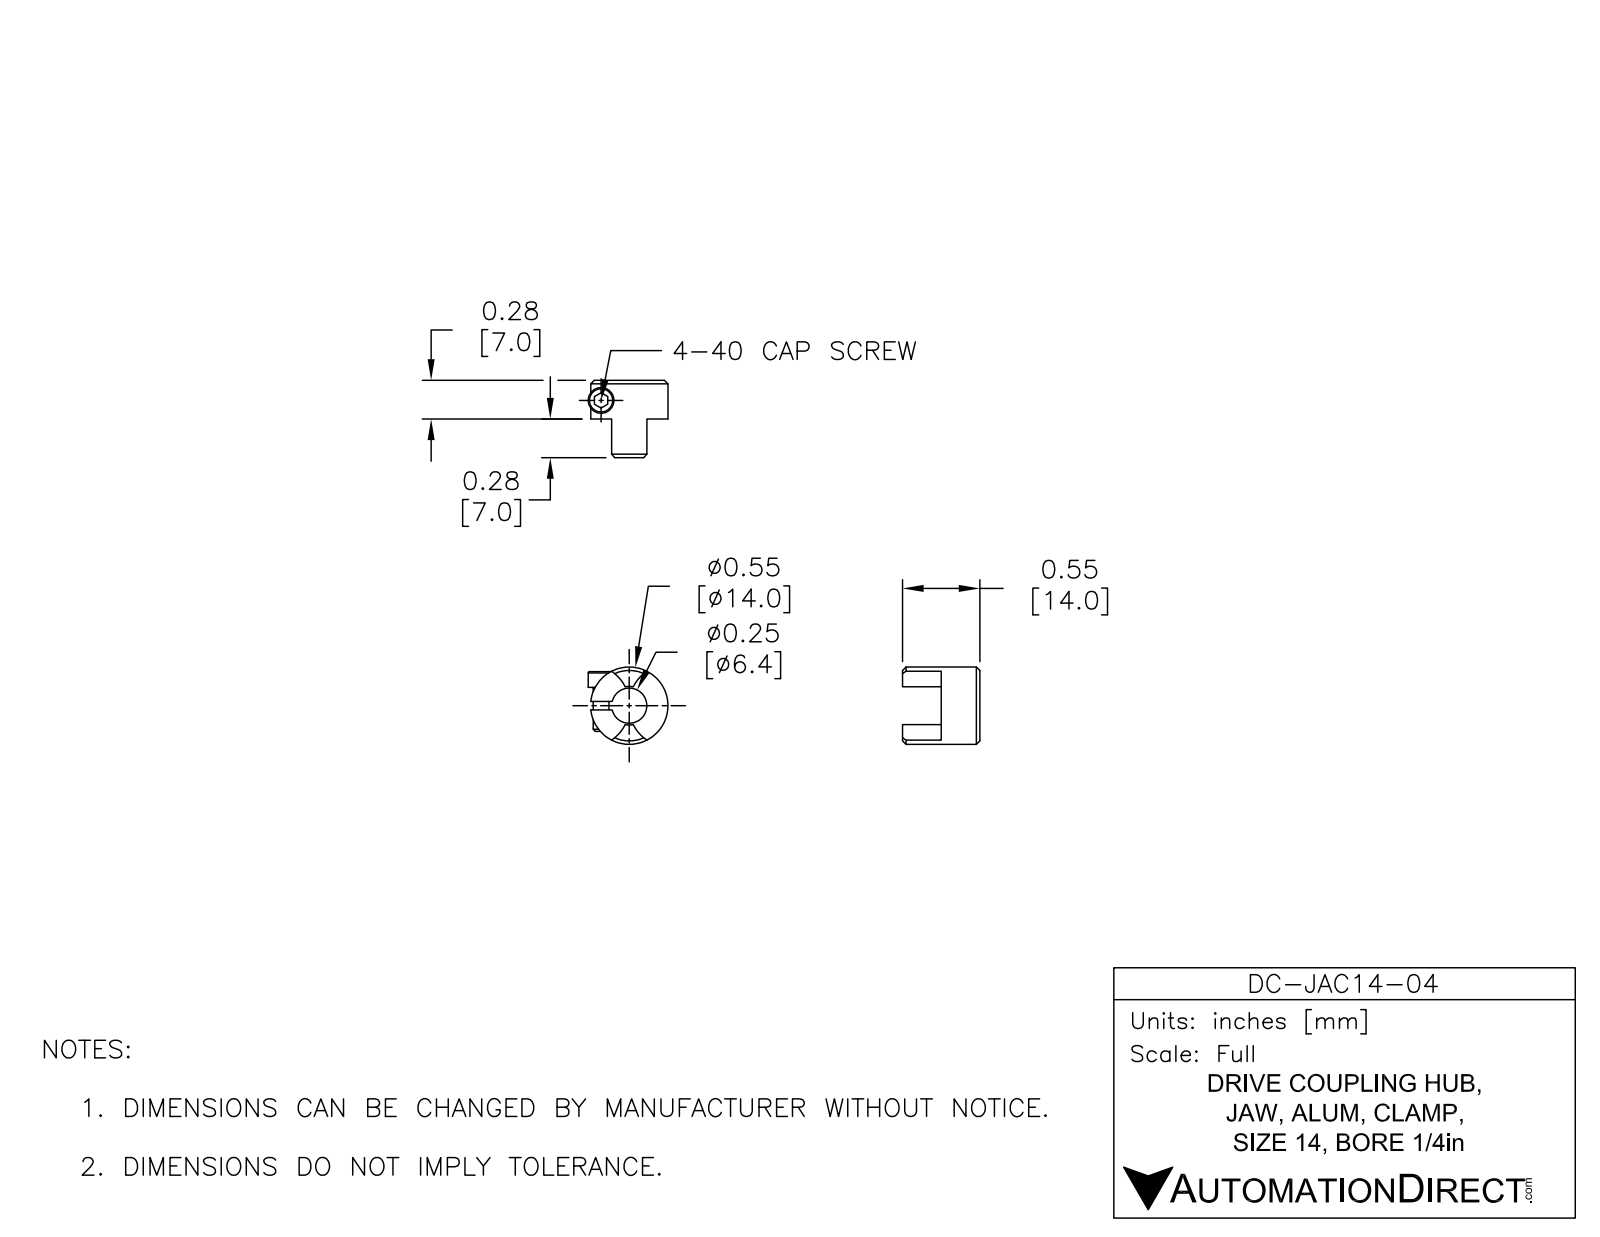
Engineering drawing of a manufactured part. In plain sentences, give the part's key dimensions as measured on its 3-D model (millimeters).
The part is named "DC-JAC14-04". Its 3-D file was written by "SolidWorks 2015 (AUTOMOTIVE_DESIGN)". It is 1 solid with 30 faces: 7 planar, 17 cylindrical and 6 other. Overall it measures 13.97 by 13.97 by 13.93 millimeters. Its volume is 901 cubic millimeters and its surface area 942 square millimeters. Round holes: 1 of diameter 3.28, 1 of diameter 6.35. Round bosses or shafts: 1 of diameter 13.97. Partial cylindrical surfaces (rounded edges, fillets, slot ends): 2 of radius 7.52, 1 of radius 2.39, 1 of radius 3.49. The main face-to-face distances are 6.99, 13.97, 6.98, 1.52, 2.54, 4.06.
